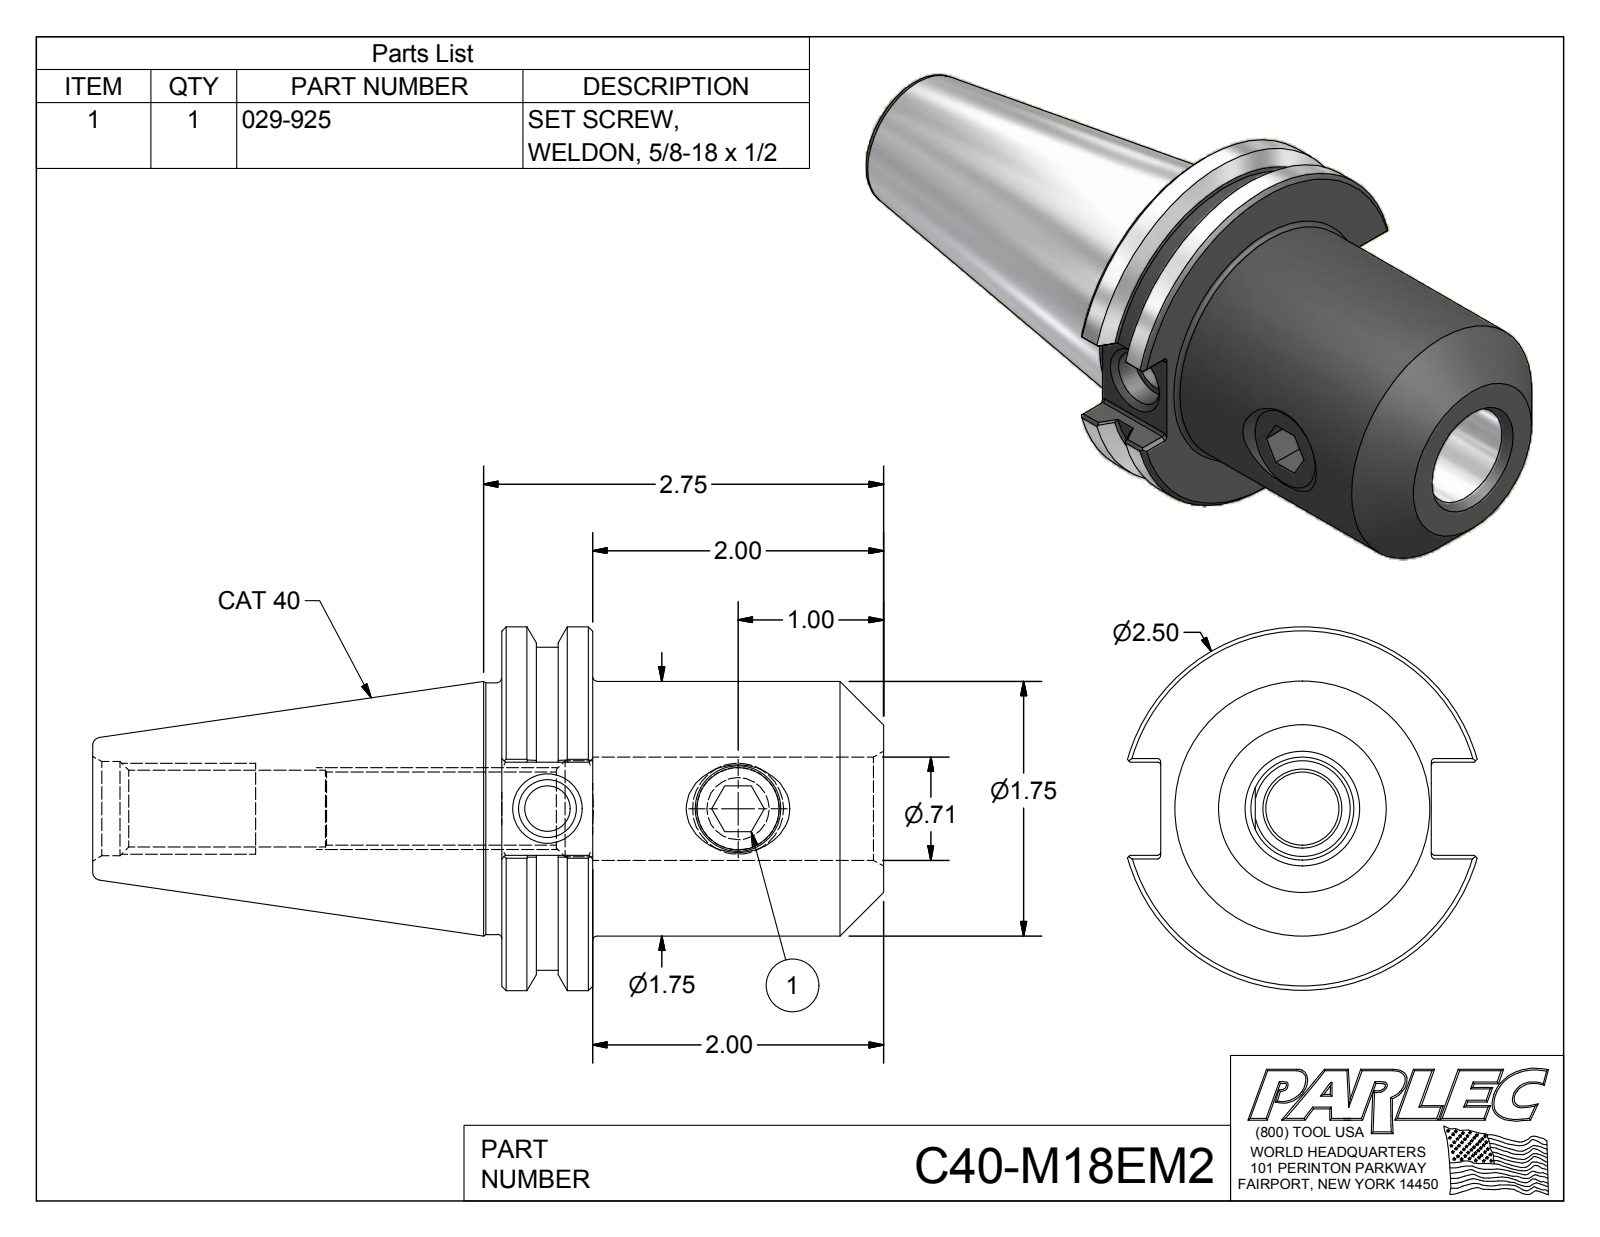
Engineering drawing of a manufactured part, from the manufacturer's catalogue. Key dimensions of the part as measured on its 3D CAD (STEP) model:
Part name (STEP PRODUCT): C40-M18EM2; C40-M18EM2-1; 029-925
STEP written by: Autodesk Inventor 2012 (AUTOMOTIVE_DESIGN)
Units: inches
Bodies: 2 solids, 103 faces (42 planar, 29 cylindrical, 32 other)
Overall size (bounding box): 5.437 × 2.5 × 2.406
Volume: 9.901 in³ · Surface area: 47.74 in²
Round holes (diameter × count): ⌀0.315 ×1, ⌀0.399 ×1, ⌀0.502 ×1, ⌀0.527 ×1, ⌀0.565 ×1, ⌀0.648 ×1, ⌀0.66 ×1, ⌀0.709 ×1
Round bosses / shafts (diameter × count): ⌀2.5 ×1, ⌀2.219 ×1, ⌀1.75 ×1, ⌀1.73 ×1, ⌀0.625 ×1
Partial cylindrical surfaces — rounded edges, fillets, slot ends (radius × count): R0.02 ×12
Main face-to-face distances: 0.625, 2.625, 2, 0.64, 0.315, 1.86, 2.812, 3.437, 5.437, 1.71
Hole centre spacings: 1.31
